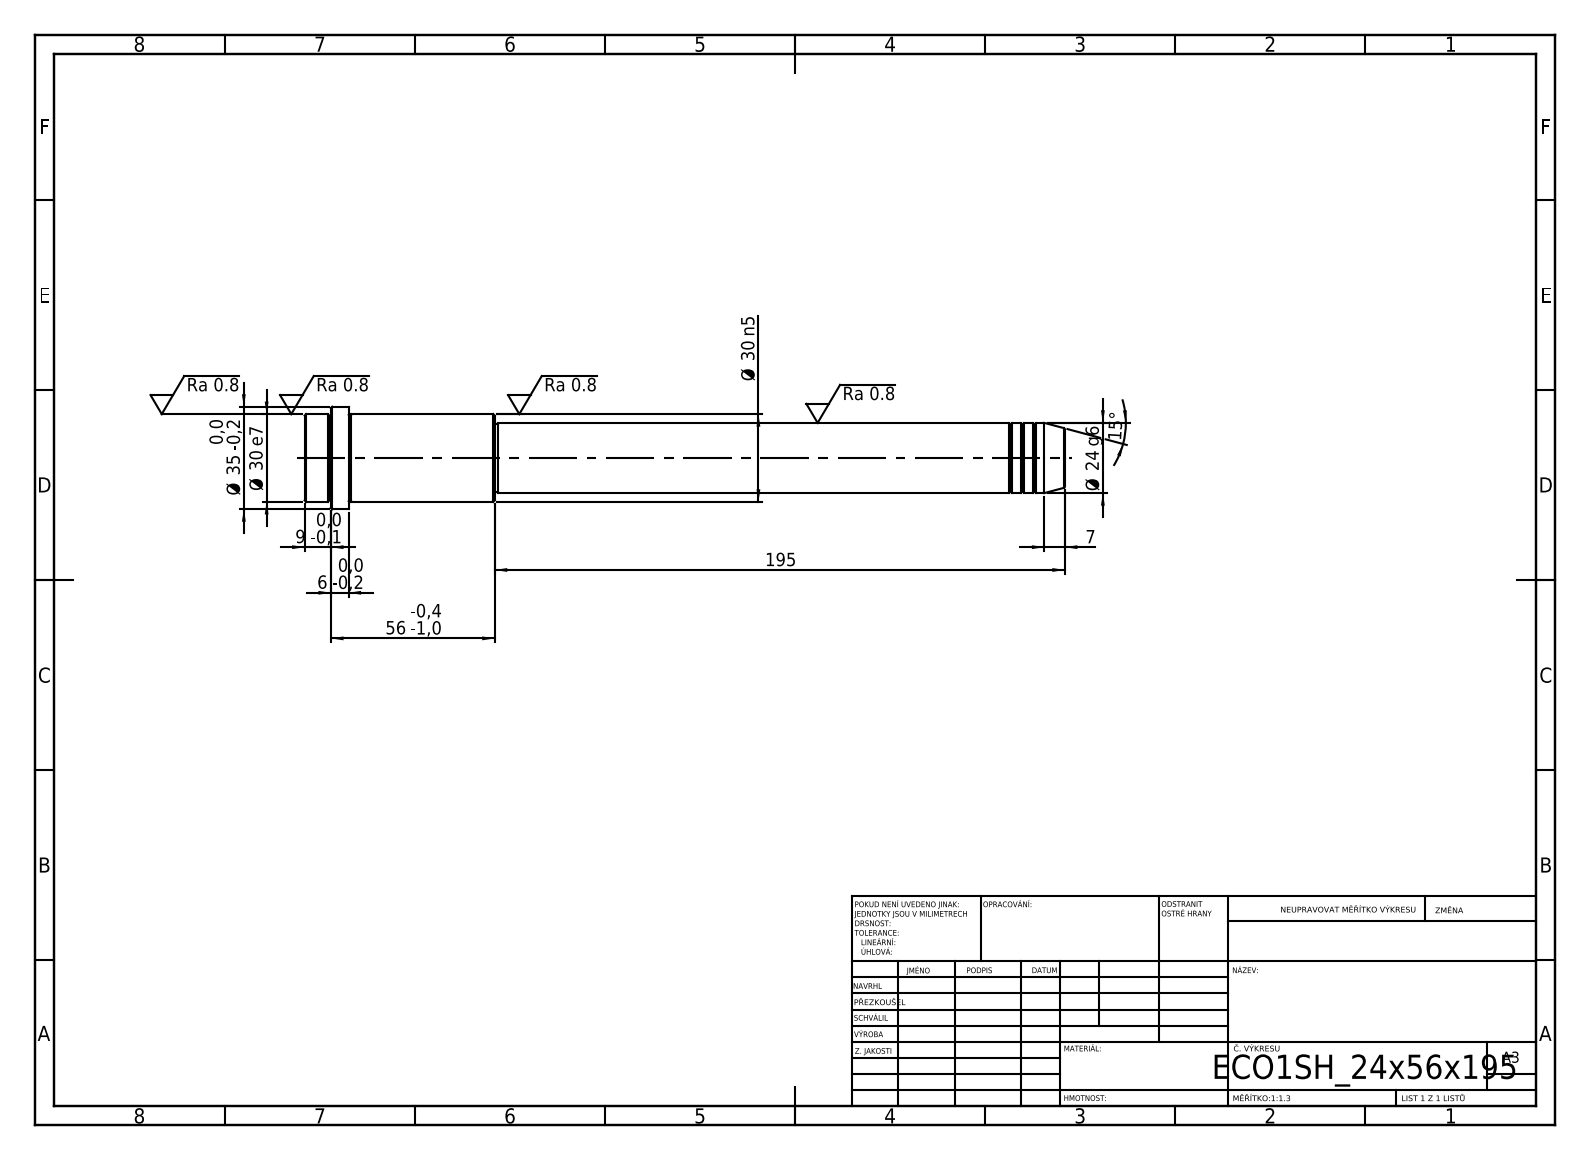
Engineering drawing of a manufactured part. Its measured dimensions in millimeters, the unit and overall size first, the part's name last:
Units: millimetres
Overall size (bounding box): 260 × 35 × 35
Round bosses / shafts (diameter × count): ⌀35 ×1, ⌀30 ×1, ⌀24 ×1, ⌀23 ×1
Main face-to-face distances: 260, 245, 15, 195, 50, 65, 251, 56, 6, 9
Volume: 134 988 mm³ · Surface area: 22 889 mm²
Bodies: 1 solid, 52 faces (6 planar, 16 cylindrical, 30 other)
STEP written by: SolidWorks 2019 (CONFIG_CONTROL_DESIGN)
